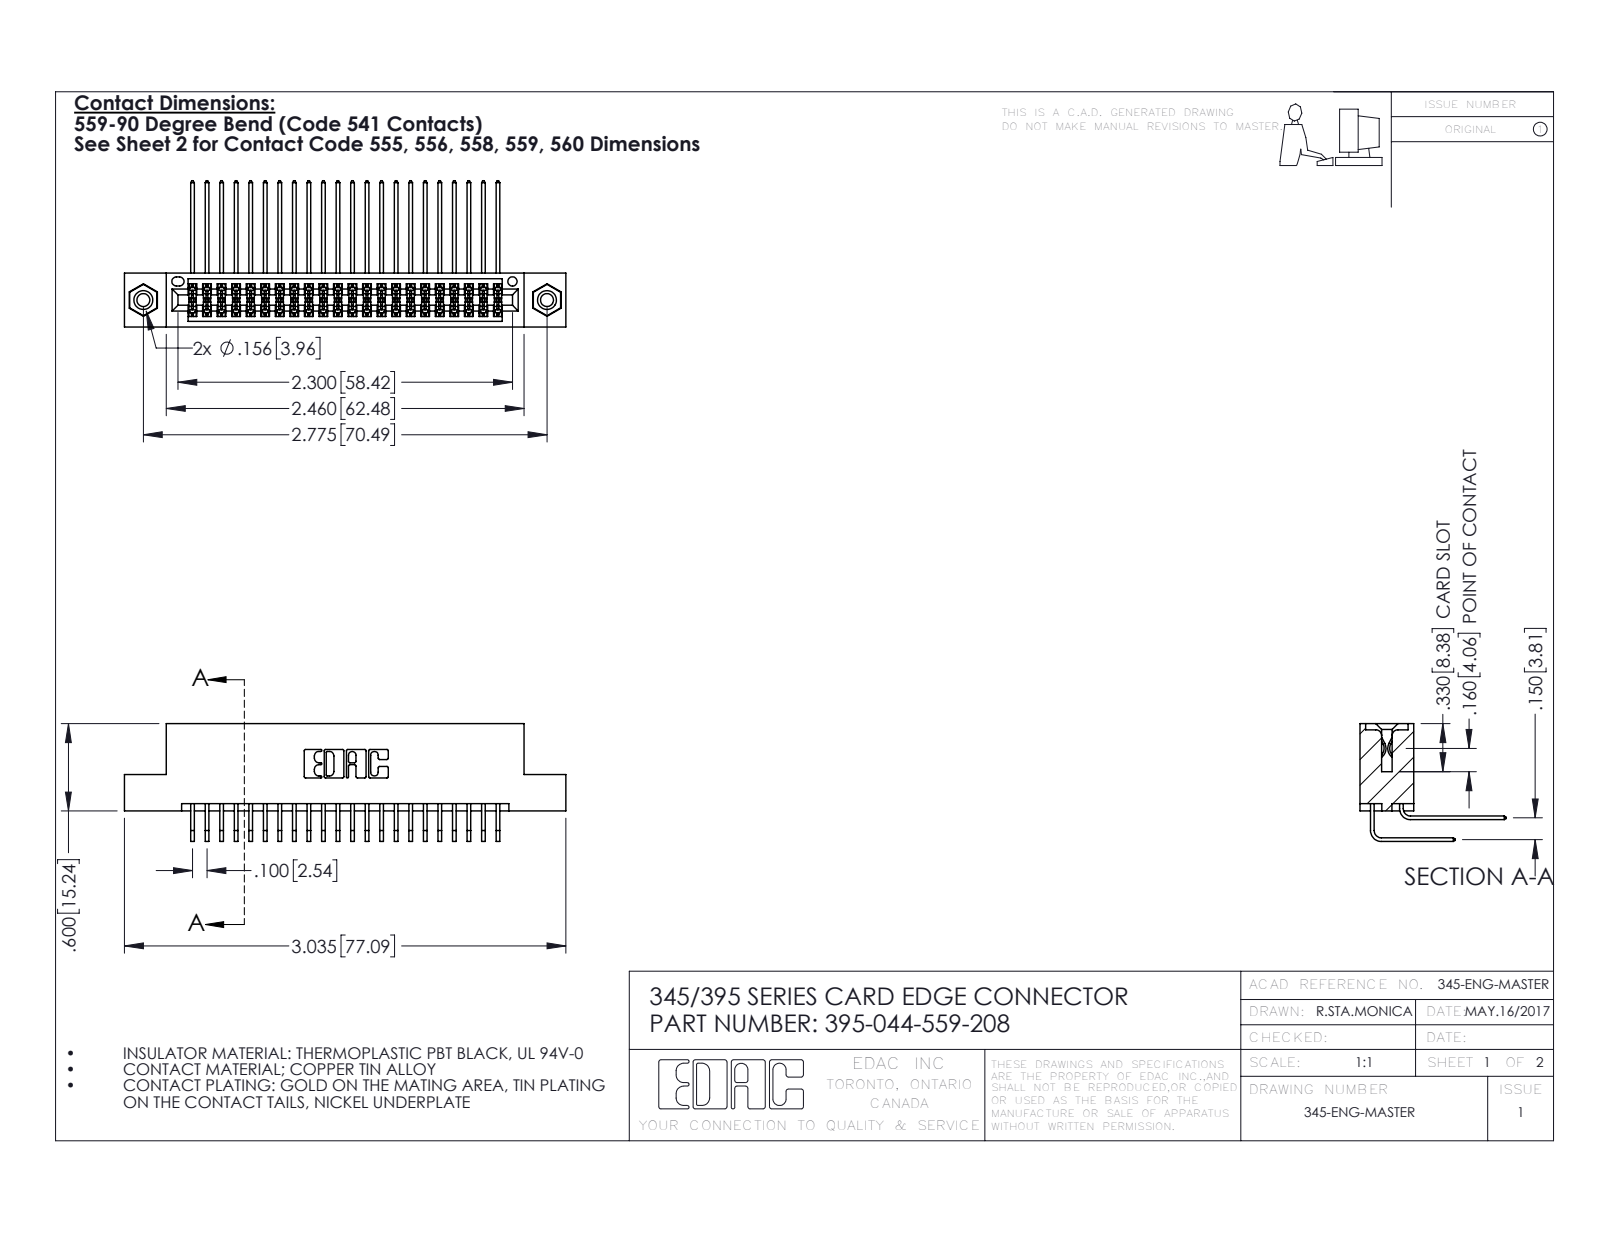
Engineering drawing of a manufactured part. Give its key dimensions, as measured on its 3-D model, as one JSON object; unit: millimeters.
{"part_name": "345-250-001_345-250-003-102; 395-044-559-208; 345-292-001_558 559 Tail - 1; 345-292-001_559 Tail - 2 (+1 more)", "step_written_by": "SolidWorks 2016 (CONFIG_CONTROL_DESIGN)", "units": "millimeters", "bodies": {"solids": 47, "faces": 2474, "planar": 1652, "cylindrical": 806, "other": 16}, "overall_size": [77.1, 25.5, 20.5], "volume_mm3": 7550, "surface_area_mm2": 11980, "round_holes": [[2.3, 2], [3.2, 2], [4, 2], [1.6, 1]], "round_bosses_or_shafts": [[3.9, 2]], "partial_cylinders_radius": [[0.2, 67], [0.3, 22], [0.2, 6], [0.8, 6], [0.7, 3], [0.4, 2], [0.5, 2], [0.6, 2]], "face_to_face_distances": [1.8, 7.6, 5.1, 9.4, 2.5, 6.9, 0.6, 5.7, 3.8, 4.4], "hole_center_spacings": [6.9, 64.5, 70.5]}
